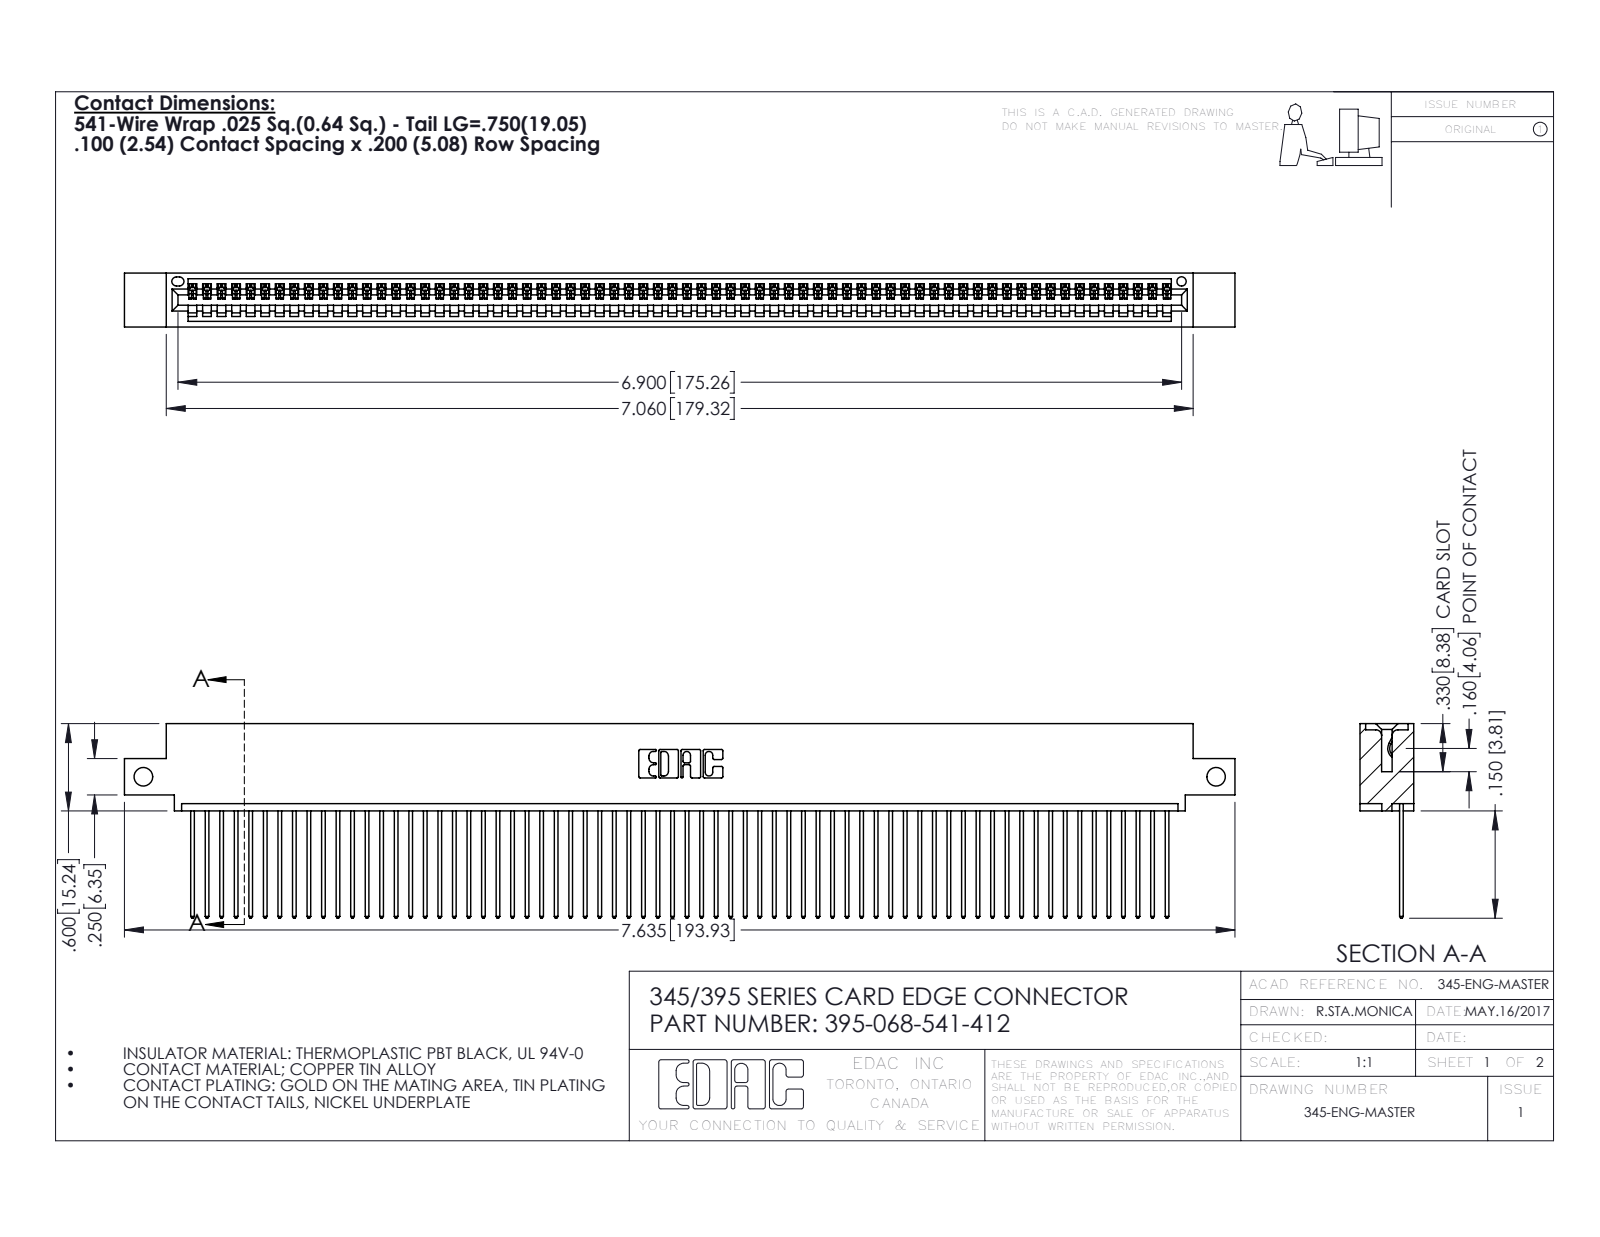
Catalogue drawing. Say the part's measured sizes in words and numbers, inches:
The part is named "345 Part_0.110 Offset - Side Mount; 395-068-541-412; 345-292-001_345-293-141". Its 3-D file was written by "SolidWorks 2016 (CONFIG_CONTROL_DESIGN)". It is 69 solids with 4074 faces: 2804 planar, 1270 cylindrical and 0 other. Overall it measures 7.635 by 1.337 by 0.37 inches. Its volume is 1.141 cubic inches and its surface area 41.01 square inches. Round holes: 2 of diameter 0.128, 1 of diameter 0.064. Partial cylindrical surfaces (rounded edges, fillets, slot ends): 136 of radius 0.006, 136 of radius 0.01, 22 of radius 0.01, 6 of radius 0.007, 6 of radius 0.031, 3 of radius 0.026, 2 of radius 0.031, 2 of radius 0.04. The main face-to-face distances are 0.072, 0.298, 0.098, 0.272, 0.025, 0.37, 0.2, 0.225, 0.149, 0.072. The hole center spacings are 7.375.
